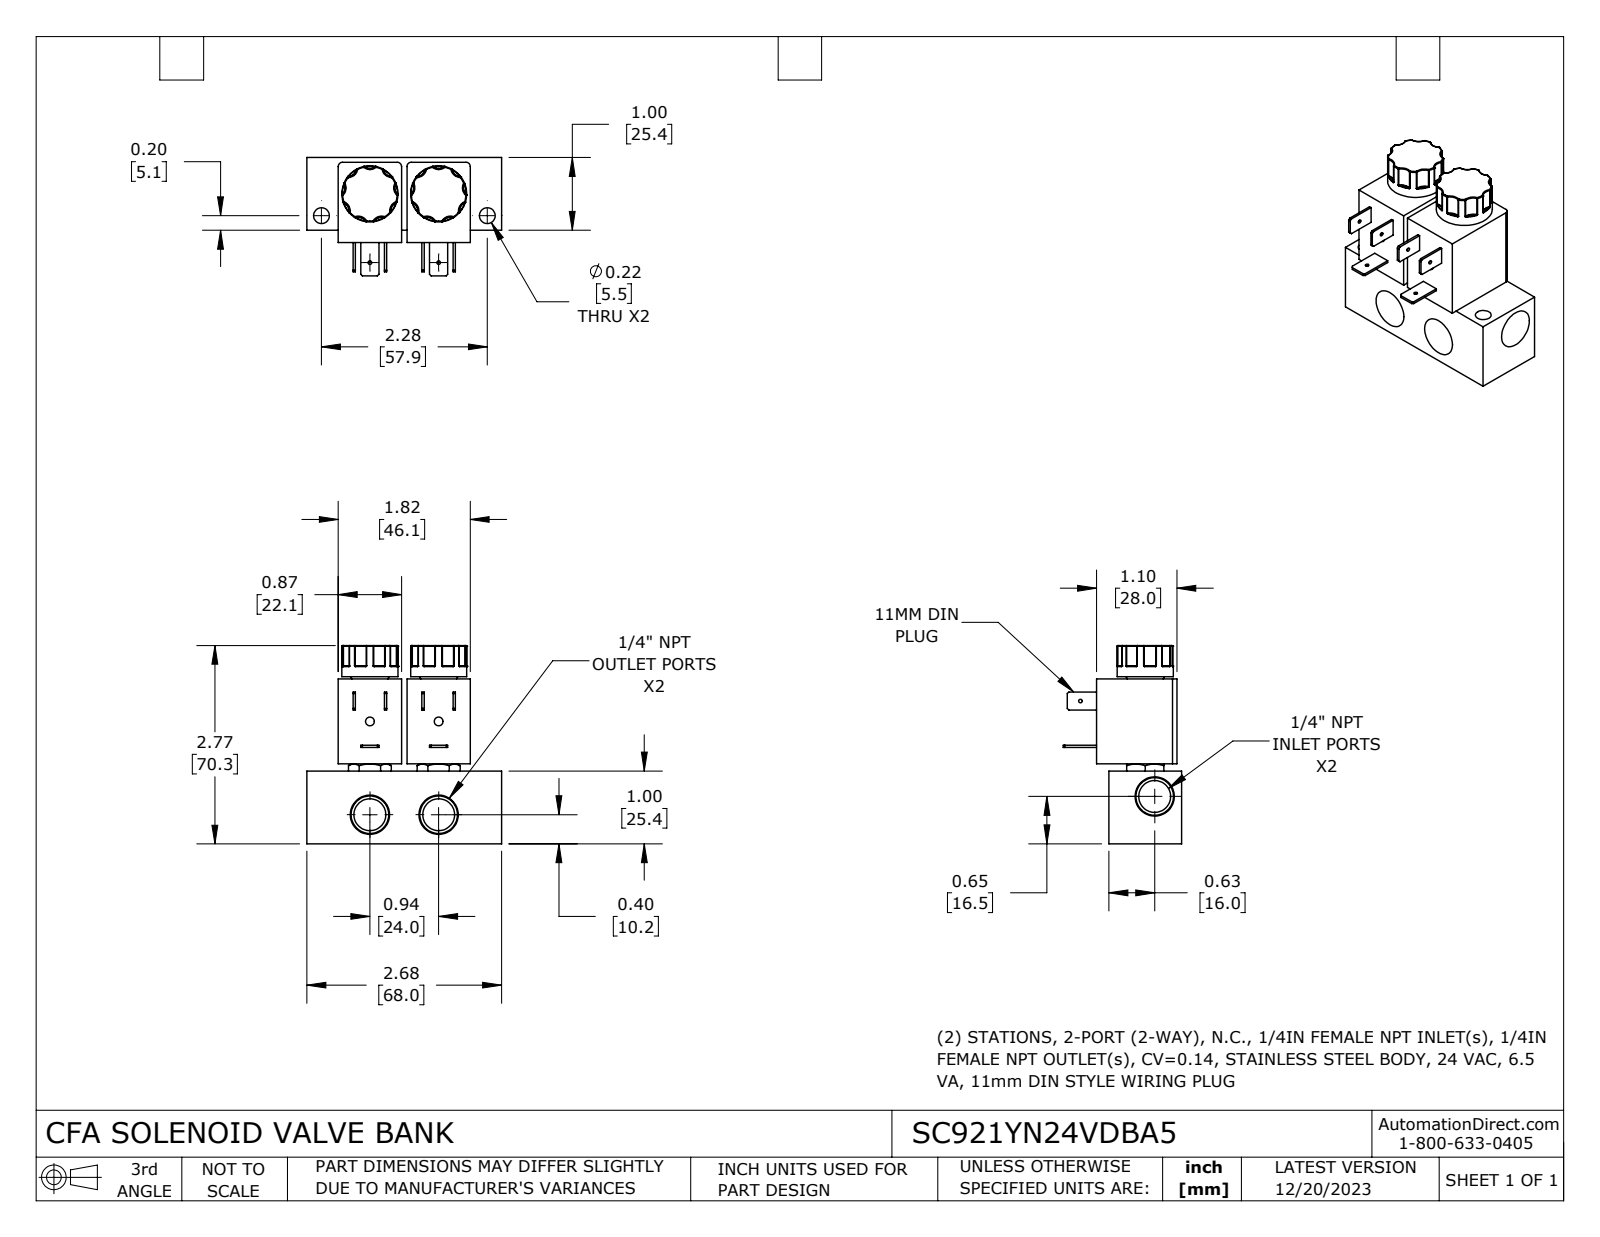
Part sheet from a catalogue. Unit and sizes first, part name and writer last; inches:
Units: inches
Overall size (bounding box): 2.725 × 2.677 × 1.627
Round holes (diameter × count): ⌀0.05 ×3, ⌀0.438 ×3, ⌀0.12 ×2, ⌀0.217 ×2
Round bosses / shafts (diameter × count): ⌀0.77 ×2
Partial cylindrical surfaces — rounded edges, fillets, slot ends (radius × count): R0.01 ×36, R0.133 ×18, R0.06 ×4
Main face-to-face distances: 1, 0.945, 0.87, 1.169, 0.169, 0.065, 0.935, 1.104, 0.431, 1.301
Hole centre spacings: 0.945, 1.282, 1.593, 0.928, 0.93, 1.662, 1.735, 1.738
Volume: 4.833 in³ · Surface area: 34.57 in²
Bodies: 1 solid, 446 faces (100 planar, 96 cylindrical, 250 other)
Part name (STEP PRODUCT): SC921YN24VDBA5
STEP written by: SolidWorks 2023 (CONFIG_CONTROL_DESIGN)
